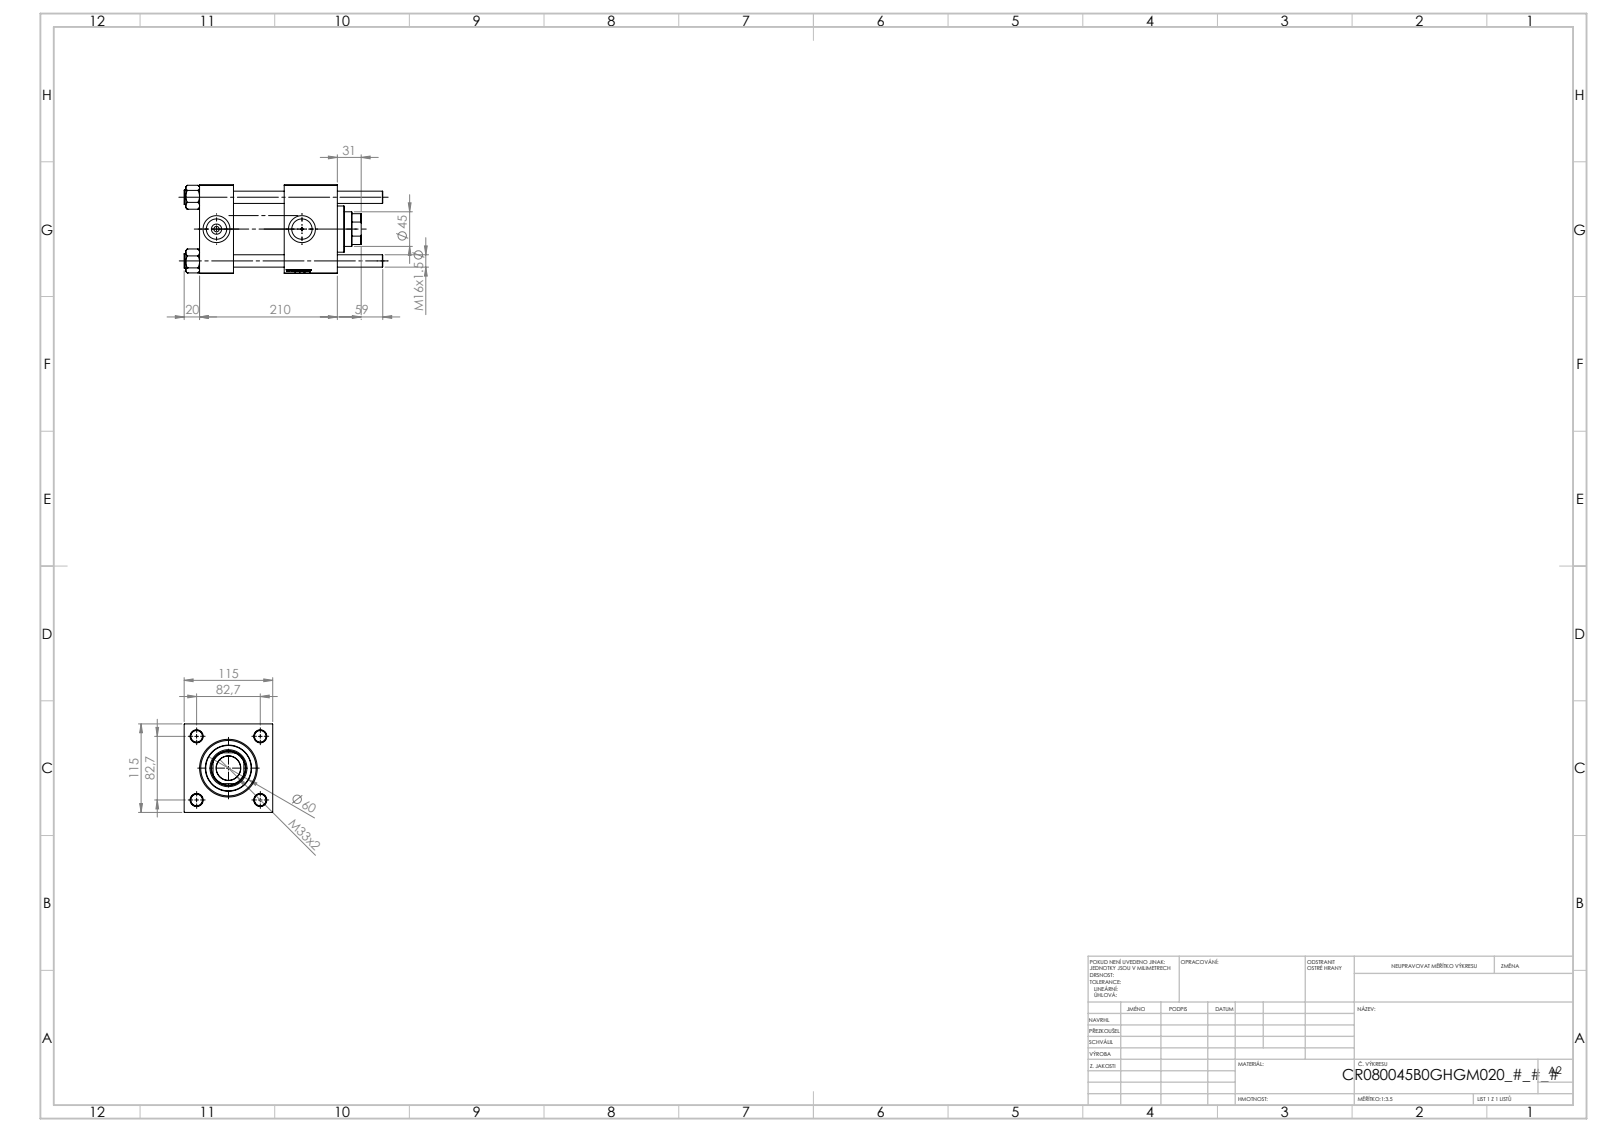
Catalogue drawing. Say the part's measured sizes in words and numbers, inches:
The part is named "V215CR_B-1; V215CR_VCP_B; V215CR_B_TYCINKA; V215_VC_A (+1 more)". Its 3-D file was written by "SolidWorks 2019 (CONFIG_CONTROL_DESIGN)". It is 11 solids with 1206 faces: 480 planar, 78 cylindrical and 648 other. Overall it measures 10.157 by 4.528 by 4.528 inches. Its volume is 115.9 cubic inches and its surface area 464.7 square inches. Round holes: 4 of diameter 0.63, 2 of diameter 0.276, 2 of diameter 1.041, 2 of diameter 1.378, 1 of diameter 1.24, 1 of diameter 1.772, 1 of diameter 1.89, 1 of diameter 2.402, 1 of diameter 2.835, 1 of diameter 3.15. Round bosses or shafts: 4 of diameter 0.748, 1 of diameter 3.386, 1 of diameter 2.362. Partial cylindrical surfaces (rounded edges, fillets, slot ends): 1 of radius 0.866. The main face-to-face distances are 4.528, 1.732, 4.331, 7.047, 5.315, 2.598, 2.717, 0.787, 5.917, 4.185. The hole center spacings are 2.302, 3.256, 4.605, 4.37.
